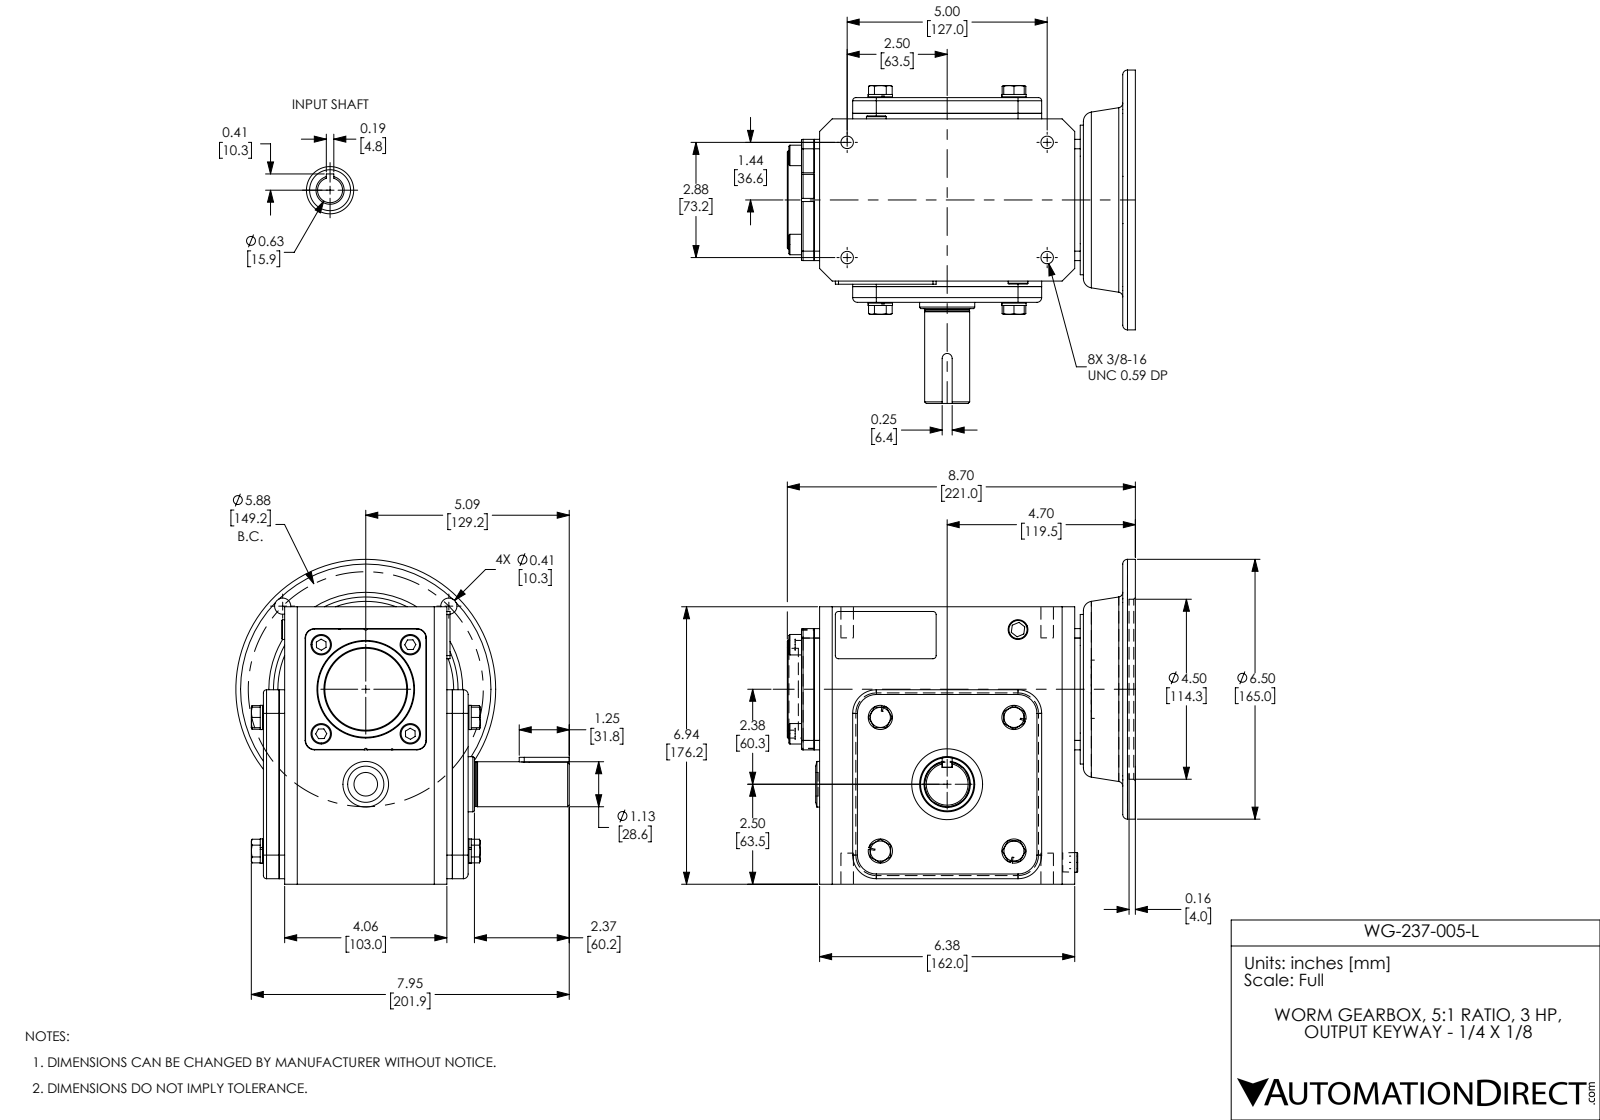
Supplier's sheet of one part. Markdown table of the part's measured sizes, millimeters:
| quantity | value |
| --- | --- |
| part name | WG-237-005-L |
| STEP written by | SolidWorks 2017 (AUTOMOTIVE_DESIGN) |
| units | millimeters |
| bodies | 37 solids, 542 faces (295 planar, 157 cylindrical, 90 other) |
| overall size | 221 × 211.7 × 206.3 |
| volume | 3 608 000 mm³ |
| surface area | 331 300 mm² |
| round holes (diameter × count) | 8 × 4, 10.3 × 4, 15 × 1, 15.9 × 1, 30 × 1, 35 × 1, 37 × 1, 45 × 1, 97 × 1, 114.3 × 1 |
| round bosses / shafts (diameter × count) | 15.4 × 4, 13 × 4, 165 × 1, 95 × 1, 62 × 1, 52 × 1, 29 × 1, 28.6 × 1 |
| partial cylindrical surfaces (radius × count) | 2 × 12, 6 × 6, 3 × 4, 15 × 4, 0.5 × 2, 1 × 2, 3.2 × 1 |
| main face-to-face distances | 3.5, 120, 10, 110, 13.5, 106.5, 116.5, 165.5, 176.2, 8 |
| hole center spacings | 74.6, 53.3, 73.2, 105.5, 105.5, 124.8, 127, 146.6 |
